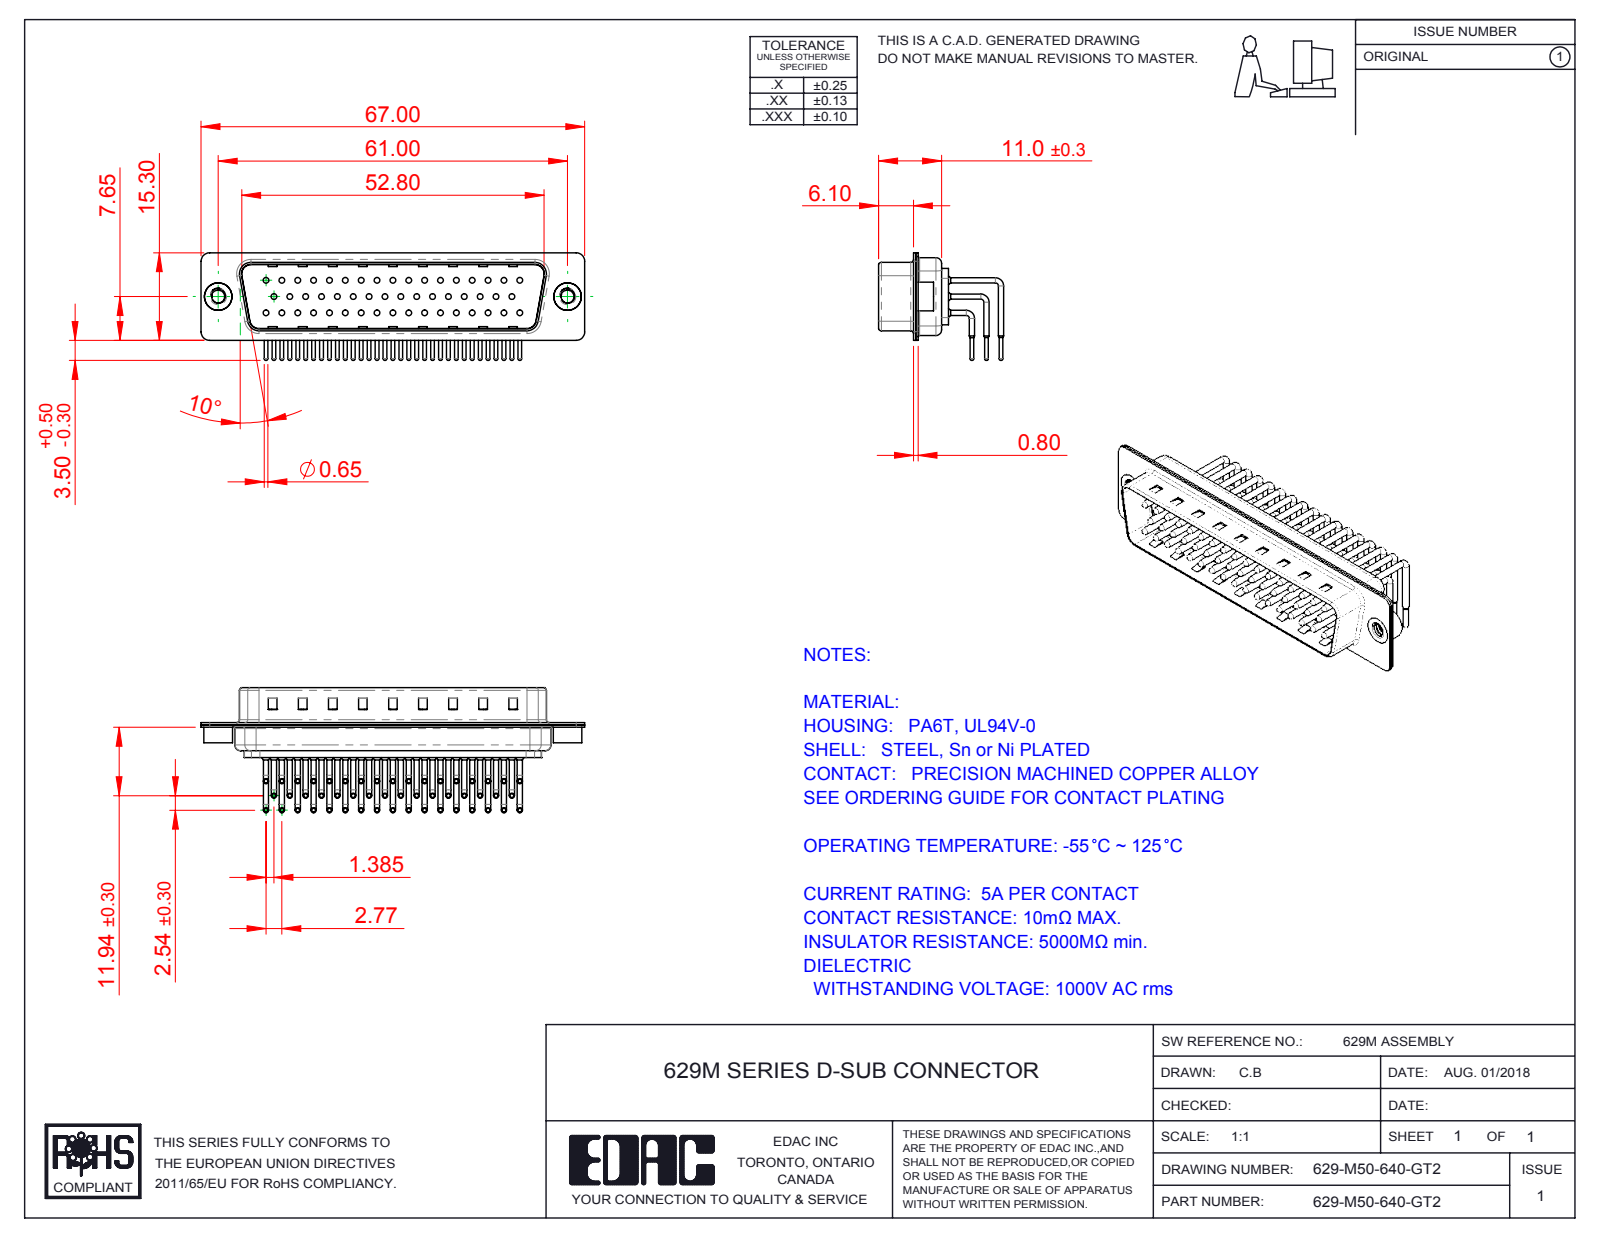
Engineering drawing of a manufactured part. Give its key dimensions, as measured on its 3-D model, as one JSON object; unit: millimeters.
{"part_name": "629M Shell Front_50 Contacts; 629M Contact Row 1_50 Contacts; 629M Shell Rear_50 Contacts; 629M Contact Row 2_50 Contacts (+4 more)", "step_written_by": "SolidWorks 2016 (CONFIG_CONTROL_DESIGN)", "units": "millimeters", "bodies": {"solids": 55, "faces": 5912, "planar": 3403, "cylindrical": 1941, "other": 568}, "overall_size": [67, 21.83, 18.8], "volume_mm3": 4991, "surface_area_mm2": 12894, "round_holes": [[1, 50], [1.7, 50], [2, 50], [2.26, 2], [4, 2], [4.8, 2]], "round_bosses_or_shafts": [[0.9, 100], [1.5, 50], [0.65, 50], [5, 2], [4.9, 2]], "partial_cylinders_radius": [[1.01, 50], [1.5, 16], [2, 12], [0.5, 8], [1.6, 8], [0.25, 4], [0.6, 4], [0.65, 4]], "face_to_face_distances": [0.4, 11.55, 5.7, 6.1, 12.38, 0.83, 0.82, 12.37, 13.2, 4.2], "hole_center_spacings": [2.77, 3.16, 5.54, 8.31, 11.08, 13.85, 16.62, 19.39]}
